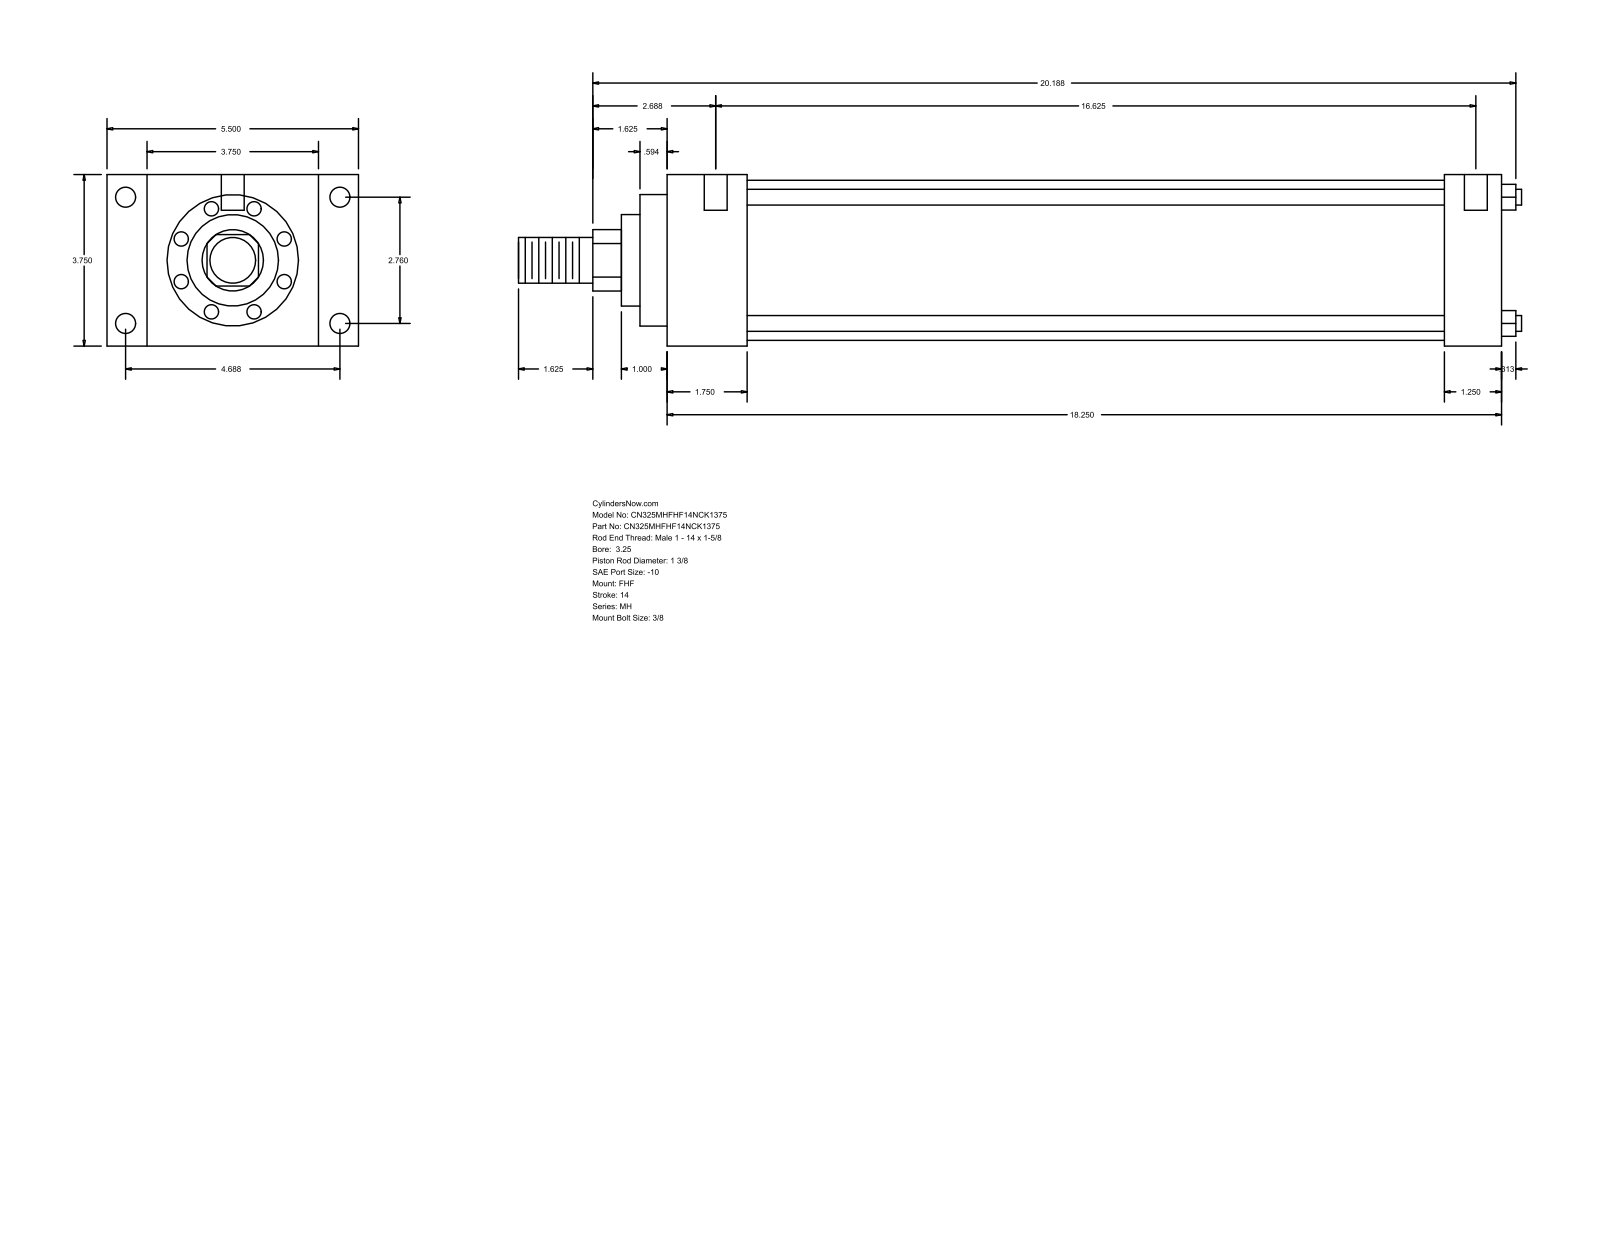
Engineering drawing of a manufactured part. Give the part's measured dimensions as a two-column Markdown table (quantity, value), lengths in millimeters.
| quantity | value |
| --- | --- |
| part name | MH_FHF__0325_1.375 |
| STEP written by | GSSL Pune (CONFIG_CONTROL_DESIGN) |
| units | millimeters |
| bodies | 0 solids, 90 faces (61 planar, 29 cylindrical, 0 other) |
| overall size | 557.21 × 139.7 × 95.25 |
| round holes (diameter × count) | 5.56 × 4, 11.13 × 4, 12.7 × 2 |
| round bosses / shafts (diameter × count) | 8.76 × 4, 88.9 × 1, 73.03 × 1, 50.8 × 1, 34.92 × 1, 25.4 × 1 |
| partial cylindrical surfaces (radius × count) | 17.06 × 1 |
| main face-to-face distances | 95.24, 463.55, 44.45, 419.1, 22.23, 117.47, 139.7, 431.8, 387.35, 31.75 |
| hole center spacings | 70.1, 119.06, 138.16, 428.63, 1.59, 4.76, 422.28, 423.87 |
